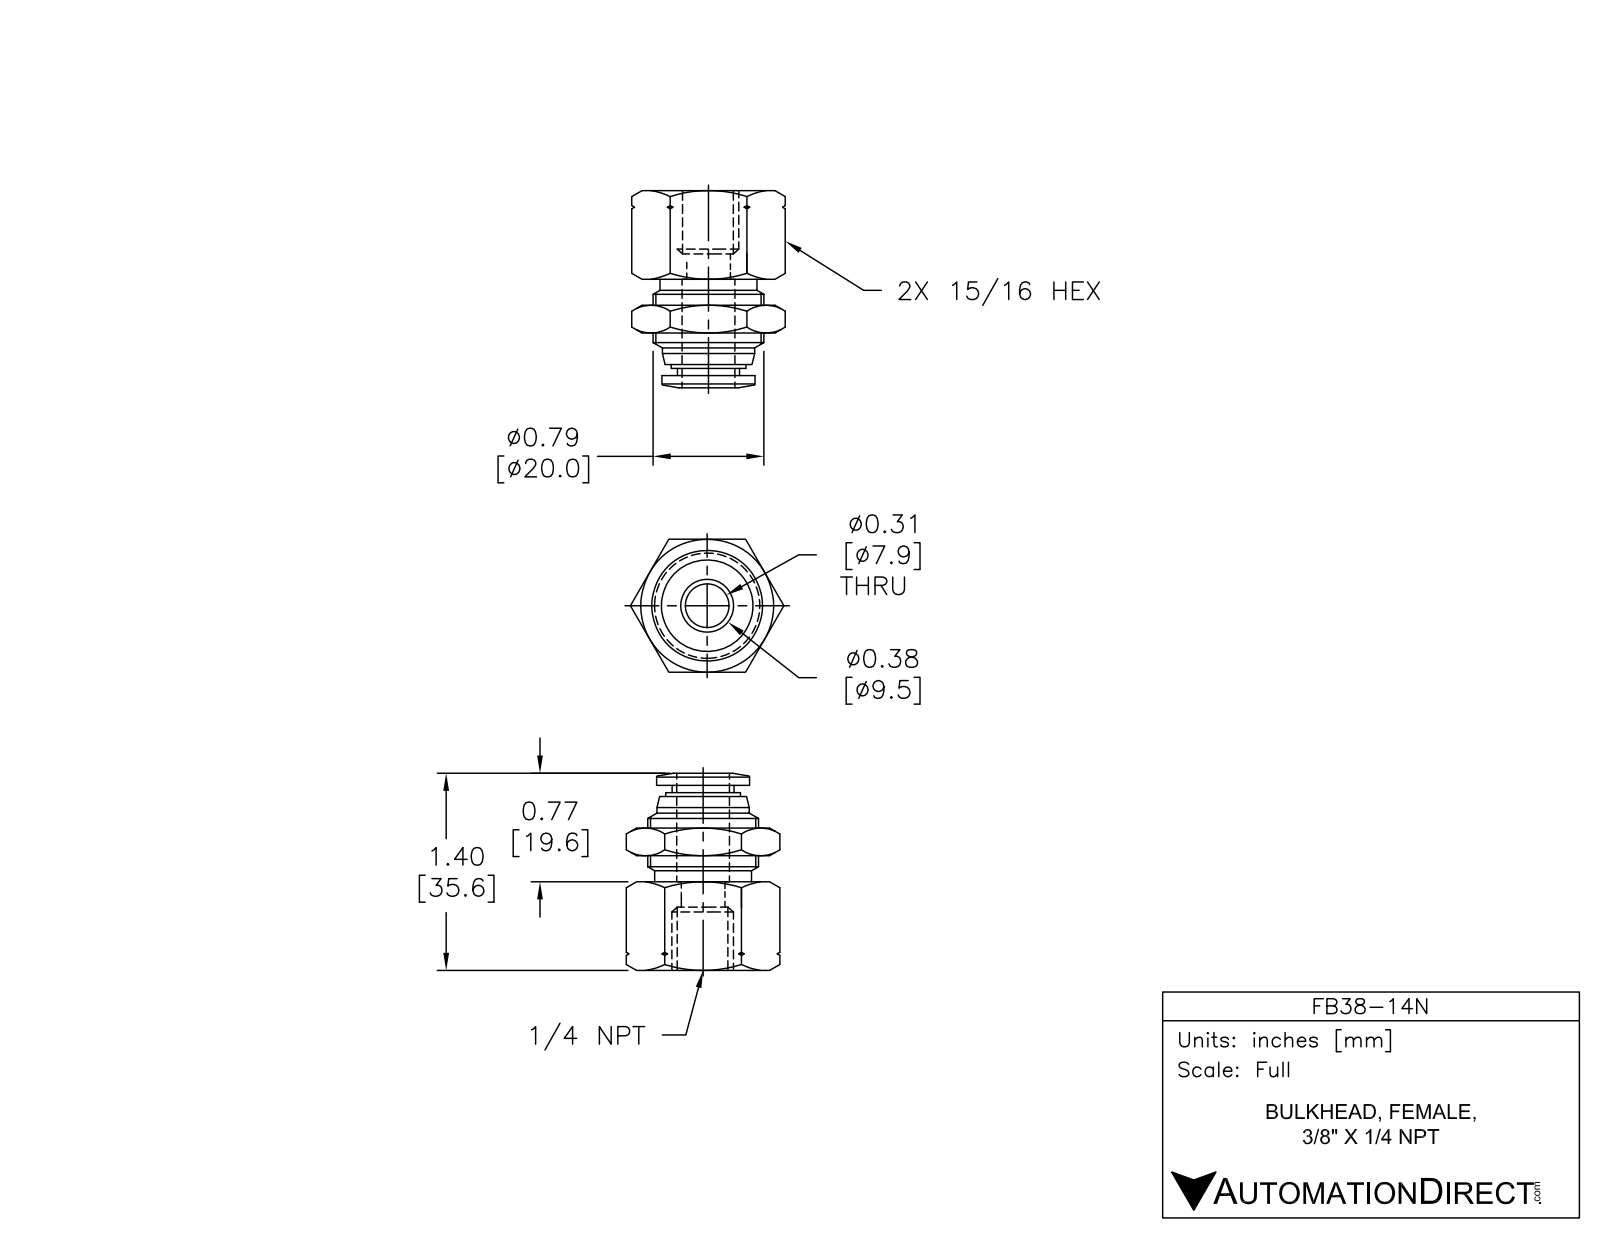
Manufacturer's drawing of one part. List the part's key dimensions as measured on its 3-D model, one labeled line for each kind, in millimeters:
Part name (STEP PRODUCT): FB38-14N
STEP written by: SolidWorks 2015 (AUTOMOTIVE_DESIGN)
Units: millimetres
Bodies: 1 solid, 91 faces (21 planar, 18 cylindrical, 52 other)
Overall size (bounding box): 35.6 × 27.7 × 24
Volume: 10 500 mm³ · Surface area: 5 198 mm²
Round holes (diameter × count): ⌀8 ×1, ⌀9.8 ×1
Round bosses / shafts (diameter × count): ⌀20 ×1, ⌀16.8 ×1, ⌀16.7 ×1, ⌀16.4 ×1, ⌀13.5 ×1, ⌀11.2 ×1
Main face-to-face distances: 24, 16, 20.5, 4.5, 25.5, 9.5, 5, 33.4, 17.4, 12.9
